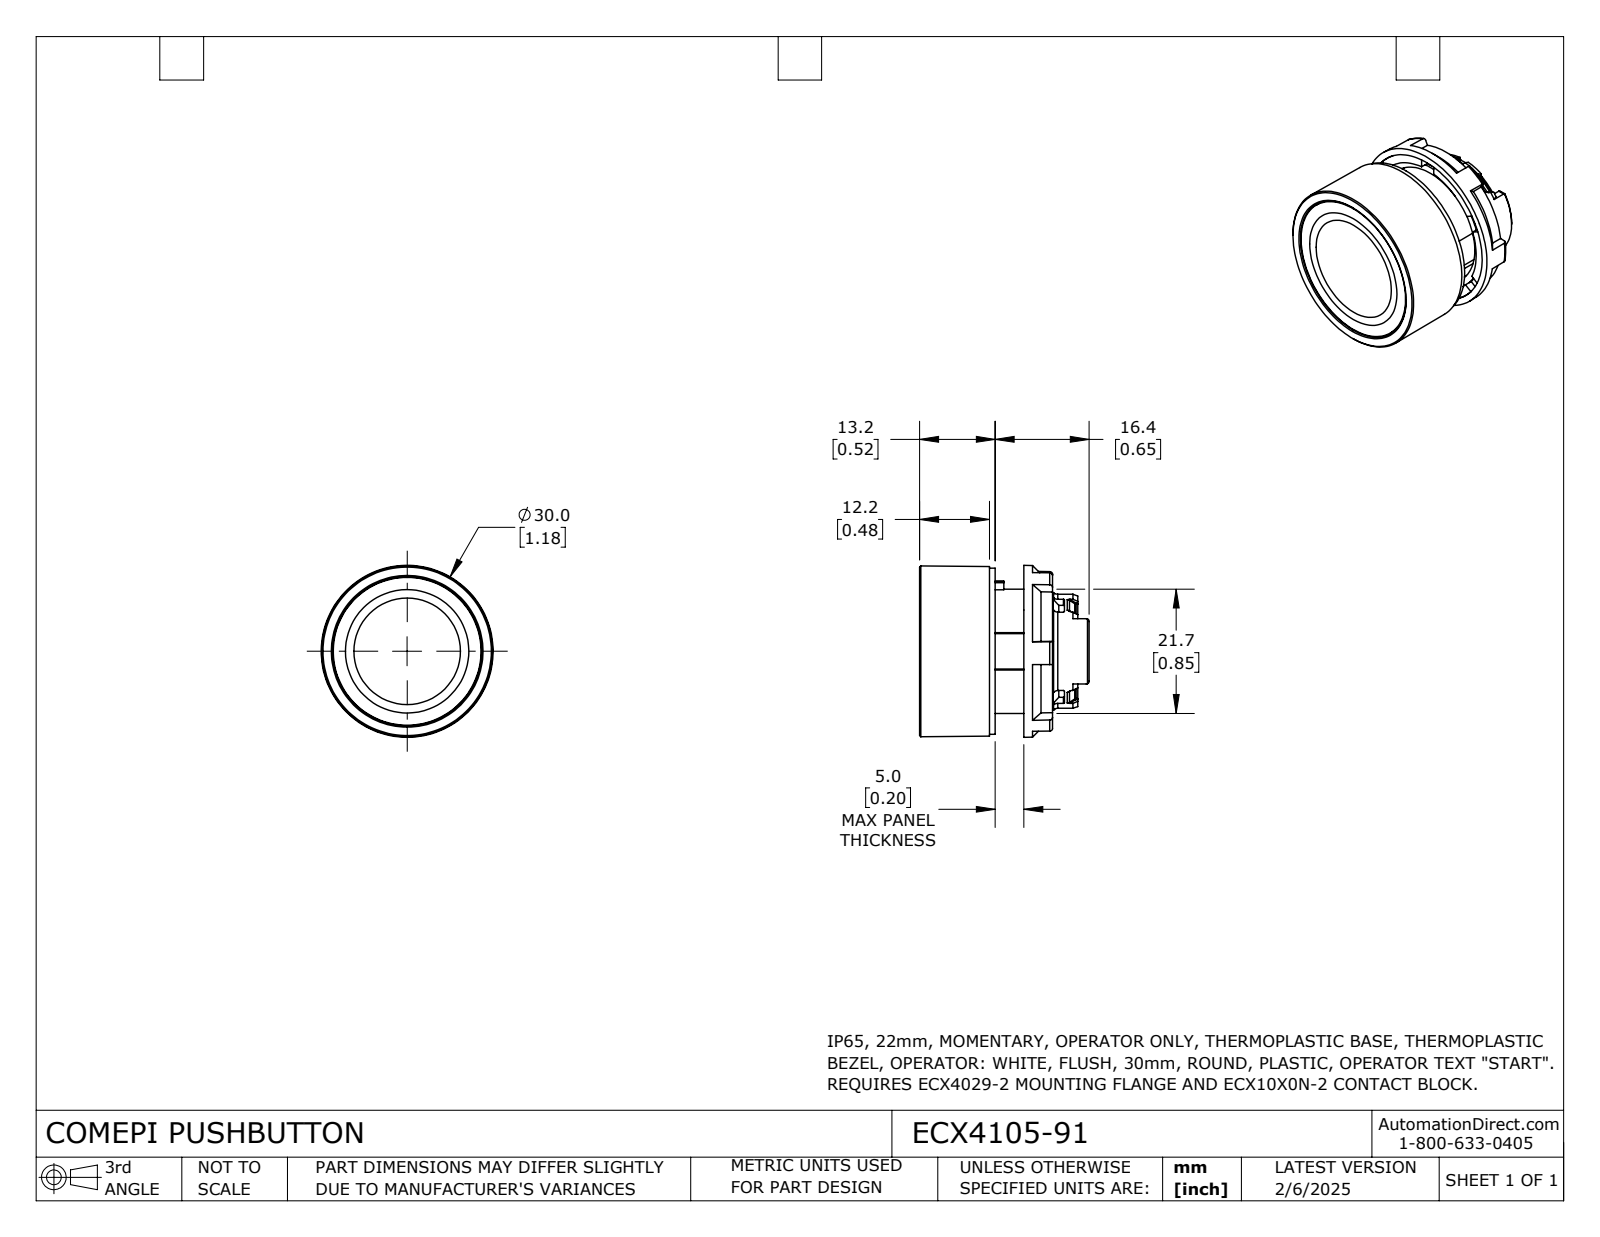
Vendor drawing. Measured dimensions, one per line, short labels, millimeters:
name: ECX4105-91
written by: SolidWorks 2024 (CONFIG_CONTROL_DESIGN)
unit: mm
bodies: 3 solids, 398 faces (134 planar, 111 cylindrical, 153 other)
size: 30 × 30 × 29.6
volume: 7 730 mm³; area: 10 680 mm²
holes: 1× ⌀13.5, 1× ⌀18.1, 1× ⌀22
bosses: 1× ⌀29, 1× ⌀25.8, 1× ⌀24.5, 1× ⌀21.7, 1× ⌀20.5, 1× ⌀20, 1× ⌀19, 1× ⌀18.5
rounds: 24× R0.2, 8× R0.5, 2× R0.3, 1× R7.4, 1× R8.7, 1× R8.8, 1× R9.3
face distances: 10.4, 1, 11, 12, 6, 10, 5, 11.4, 13, 5.5
